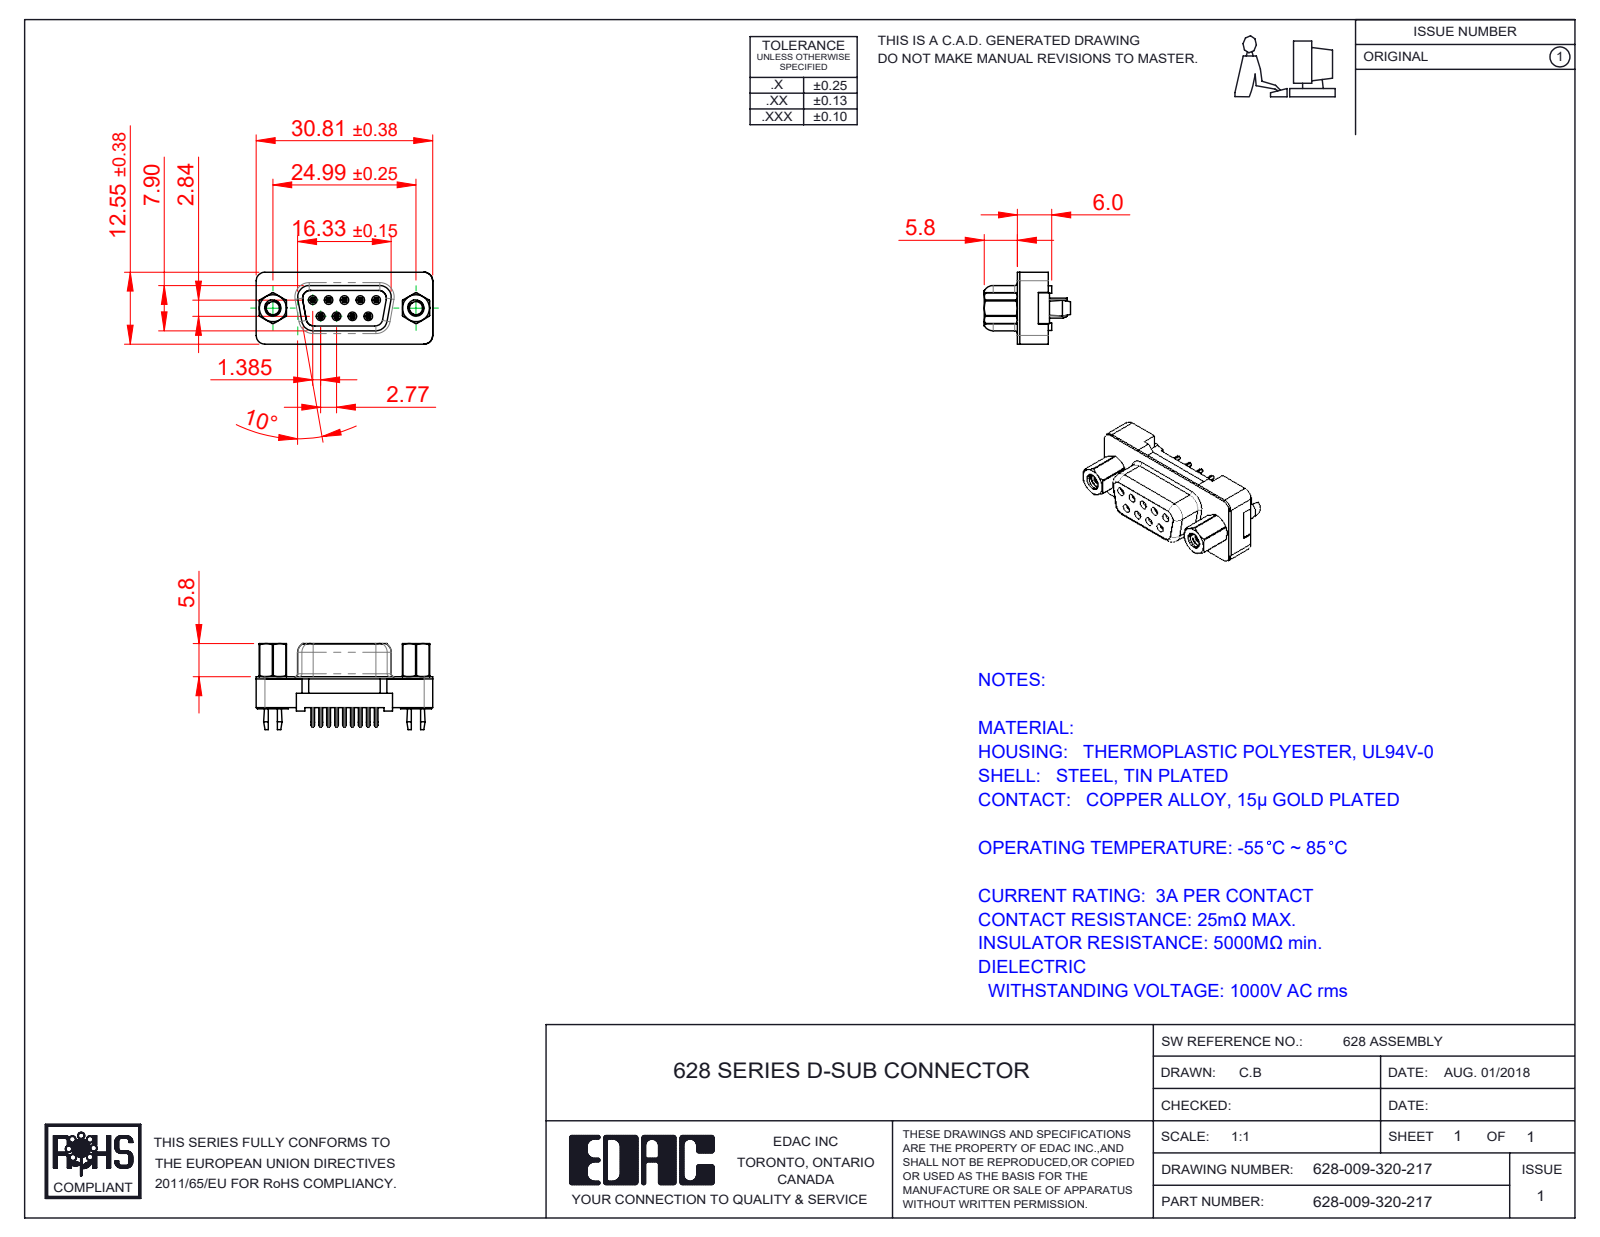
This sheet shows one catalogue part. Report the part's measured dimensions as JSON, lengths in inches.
{"part_name": "628 PB Contact Row 1_20; 628 PB Shell_09 Contacts; 628 4-40 Hex Standoff; 628 Plastic Body Housing_09 Contacts (+3 more)", "step_written_by": "SolidWorks 2020 (CONFIG_CONTROL_DESIGN)", "units": "inches", "bodies": {"solids": 15, "faces": 1053, "planar": 410, "cylindrical": 314, "other": 329}, "overall_size": [1.213, 0.593, 0.494], "volume_in3": 0.134, "surface_area_in2": 7.66, "round_holes": [[0.035, 9], [0.089, 2], [0.09, 2], [0.12, 2], [0.157, 2], [0.189, 2], [0.197, 2]], "round_bosses_or_shafts": [[0.193, 2], [0.11, 2]], "partial_cylinders_radius": [[0.01, 36], [0.02, 13], [0.053, 11], [0.012, 9], [0.059, 8], [0.035, 4], [0.063, 4], [0.069, 4]], "face_to_face_distances": [0.016, 0.079, 0.218, 0.109, 0.098, 0.244, 0.197, 0.213, 0.343, 0.106], "hole_center_spacings": [0.124, 0.109, 0.218, 0.198, 0.198, 0.327, 0.28, 0.294]}
